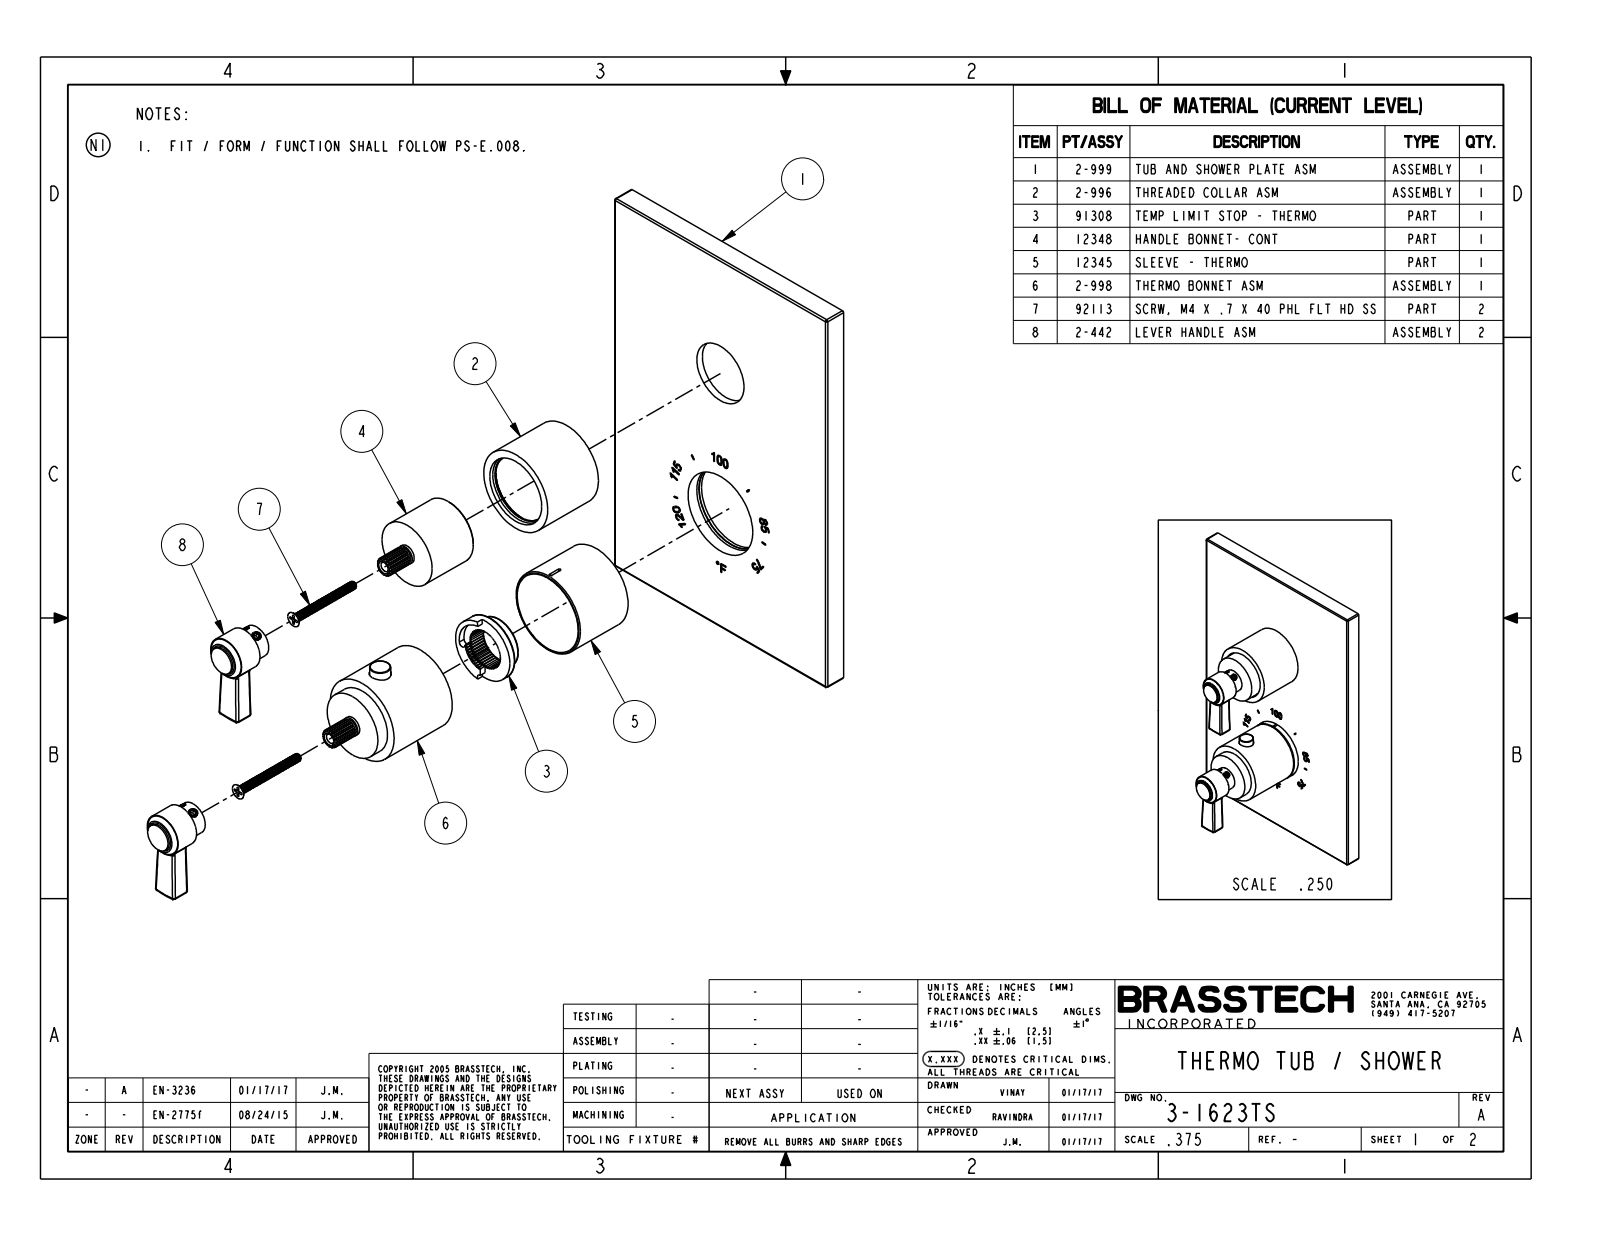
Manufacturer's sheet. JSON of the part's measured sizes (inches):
{"part_name": "12349_AF2; H-78_2_FEET_AF8; 91678; 2-999_AF2_ASM (+8 more)", "step_written_by": "PRO/ENGINEER BY PARAMETRIC TECHNOLOGY CORPORATION, 2013150 (CONFIG_CONTROL_DESIGN)", "units": "inches", "bodies": {"solids": 22, "faces": 2375, "planar": 873, "cylindrical": 633, "other": 869}, "overall_size": [8.25, 5.5, 4.011], "volume_in3": 9.861, "surface_area_in2": 353.1, "round_holes": [[0.136, 4], [0.19, 2], [0.276, 2], [0.339, 2], [0.063, 1], [0.079, 1], [0.1, 1], [0.126, 1], [0.406, 1], [1.015, 1], [1.15, 1], [1.22, 1]], "round_bosses_or_shafts": [[0.164, 4], [0.157, 3], [1.654, 2], [0.8, 2], [0.625, 2], [0.525, 2], [0.512, 2], [0.37, 2]], "partial_cylinders_radius": [[0.03, 8], [0.04, 8], [0.5, 8], [0.039, 2], [0.075, 2], [0.082, 2], [0.125, 2], [0.164, 2]], "face_to_face_distances": [0.08, 0.248, 0.168, 0.08, 0.25, 0.33, 5.5, 5.42, 0.19, 0.358], "hole_center_spacings": [1.618, 0.554, 1.144, 1.696, 2.596, 2.596, 3.15, 3.15]}
